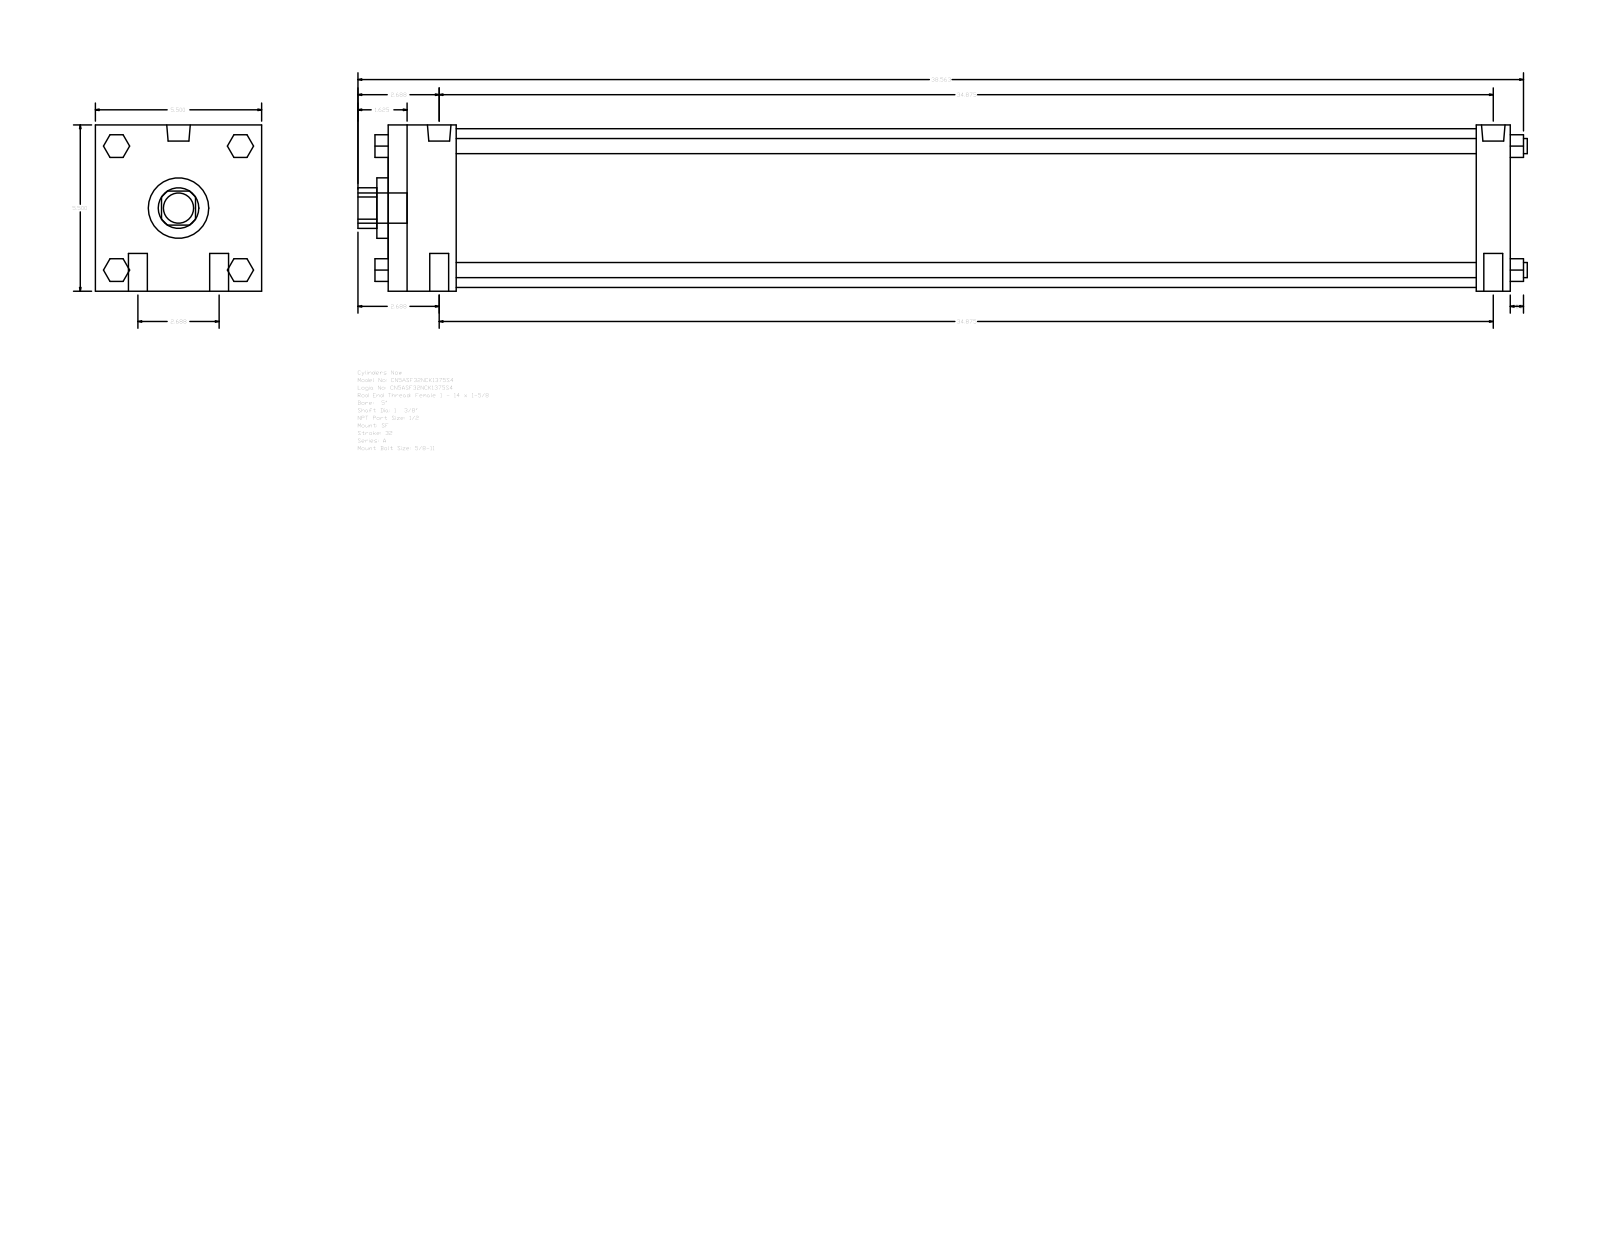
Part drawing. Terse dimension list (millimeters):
name: A_SF__0500_1.375
written by: GSSL Pune (CONFIG_CONTROL_DESIGN)
unit: mm
bodies: 0 solids, 124 faces (94 planar, 30 cylindrical, 0 other)
size: 982.66 × 139.7 × 139.7
holes: 1× ⌀34.92, 1× ⌀50.8, 1× ⌀133.35
bosses: 4× ⌀15.88, 4× ⌀12.7, 2× ⌀19.77, 2× ⌀8.73, 1× ⌀25.4
rounds: 1× R17.06
face distances: 139.7, 942.98, 28.58, 57.15, 914.4, 857.25, 885.83, 19.05, 52.07, 90.18
